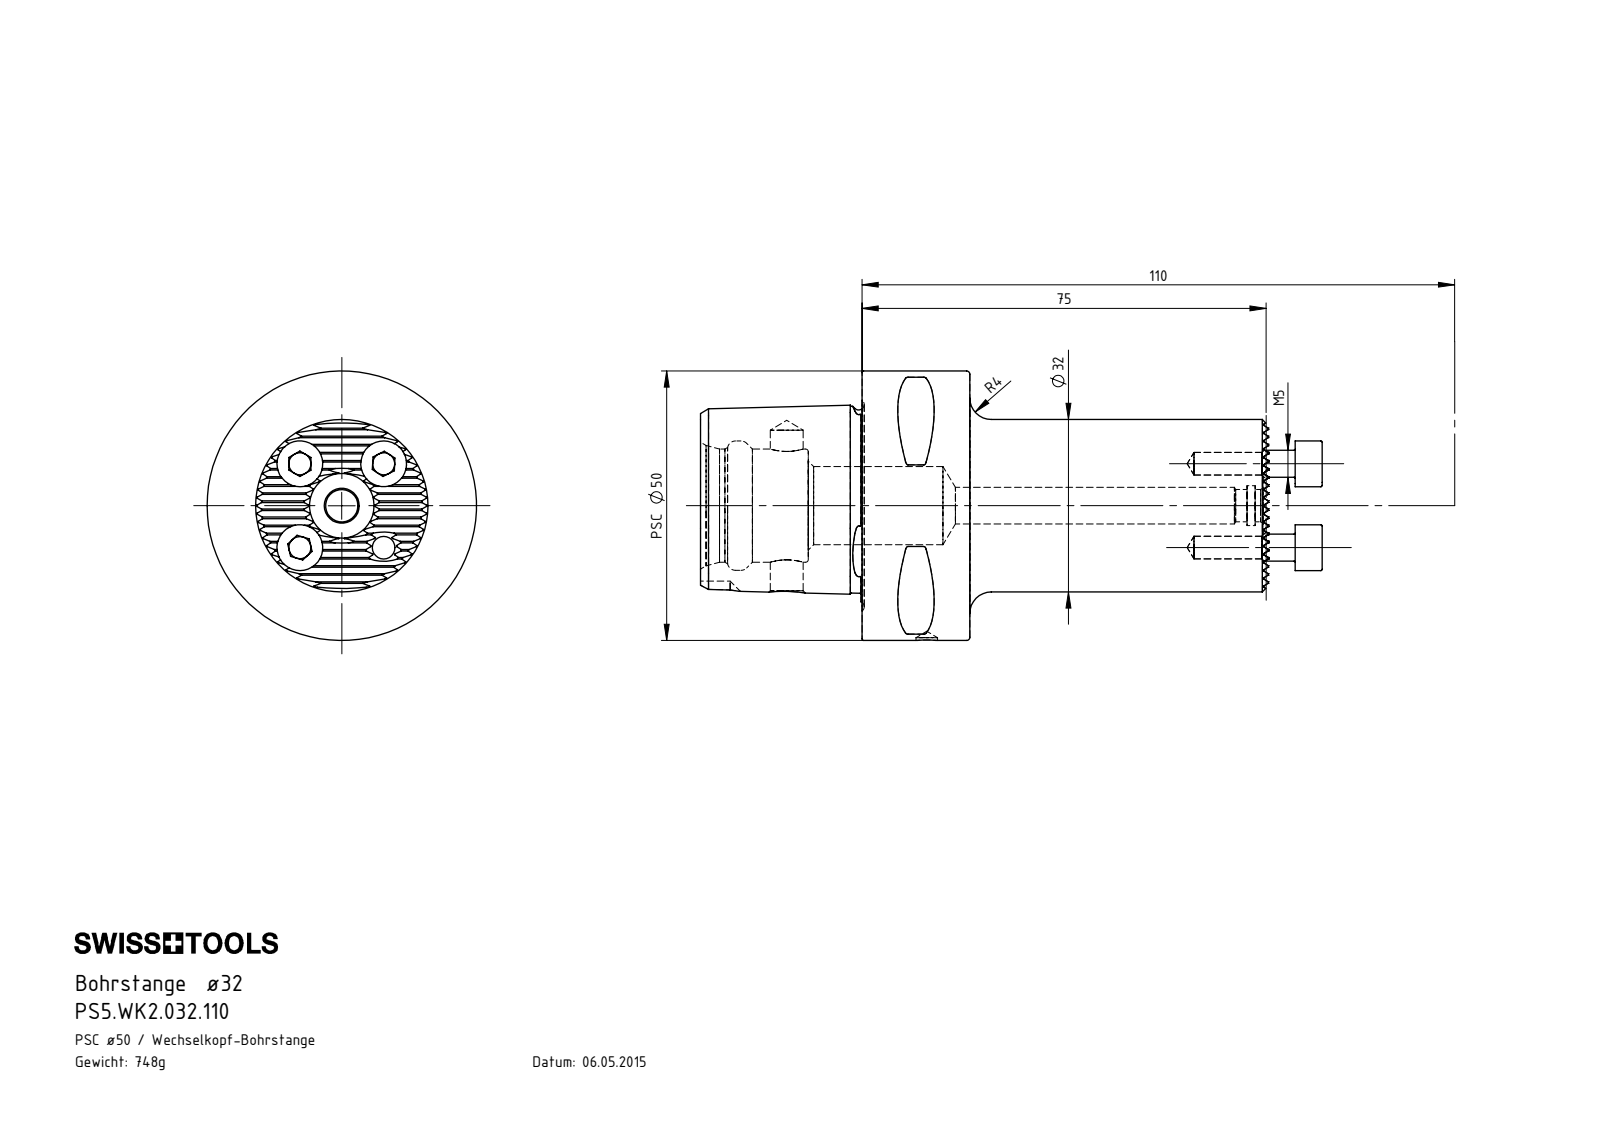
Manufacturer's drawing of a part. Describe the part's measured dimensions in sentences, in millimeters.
The part is named "PS5.WK2.032.110; DIN 3771 - 6x1; PS5-WK2.032.110_B; ISO 4762 - M5 x 14". Its 3-D file was written by "SolidWorks 2017 (AUTOMOTIVE_DESIGN)". It is 5 solids with 421 faces: 197 planar, 97 cylindrical and 127 other. Overall it measures 115.4 by 50 by 50 millimeters. Its volume is 96 697 cubic millimeters and its surface area 22 091 square millimeters. Round holes: 4 of diameter 4.2, 1 of diameter 4, 1 of diameter 6, 1 of diameter 6.1, 1 of diameter 6.8, 1 of diameter 7.4, 1 of diameter 14.5, 1 of diameter 21, 1 of diameter 24. Round bosses or shafts: 3 of diameter 8.5, 3 of diameter 5, 1 of diameter 50, 1 of diameter 32. Partial cylindrical surfaces (rounded edges, fillets, slot ends): 21 of radius 0.12, 8 of radius 0.5, 1 of radius 4. The main face-to-face distances are 20, 1.3, 2.6, 30, 3.9, 5.2, 50, 12.99, 6.5, 11.69. The hole center spacings are 11, 15.56, 22.01, 26.
